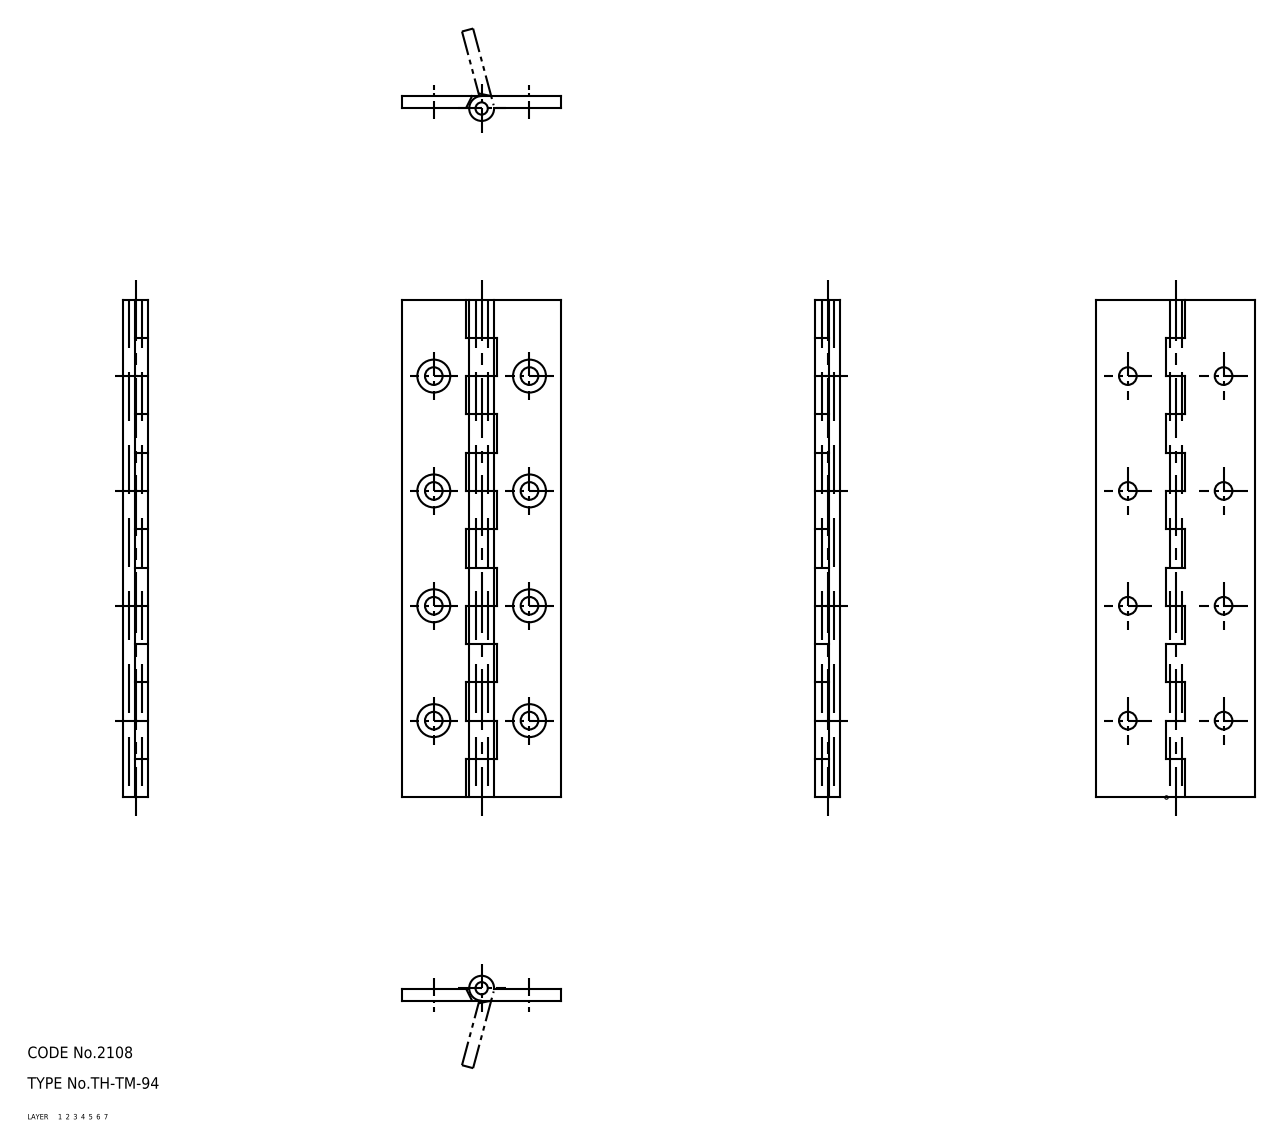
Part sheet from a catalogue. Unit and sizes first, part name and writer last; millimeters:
Units: millimetres
Overall size (bounding box): 130 × 41.5 × 6.5
Volume: 17 560 mm³ · Surface area: 16 306 mm²
Bodies: 3 solids, 135 faces (0 planar, 0 cylindrical, 135 other)
Part name (STEP PRODUCT): 67117179; 67117192; 67117205
STEP written by: CADfix (AUTOMOTIVE_DESIGN)
